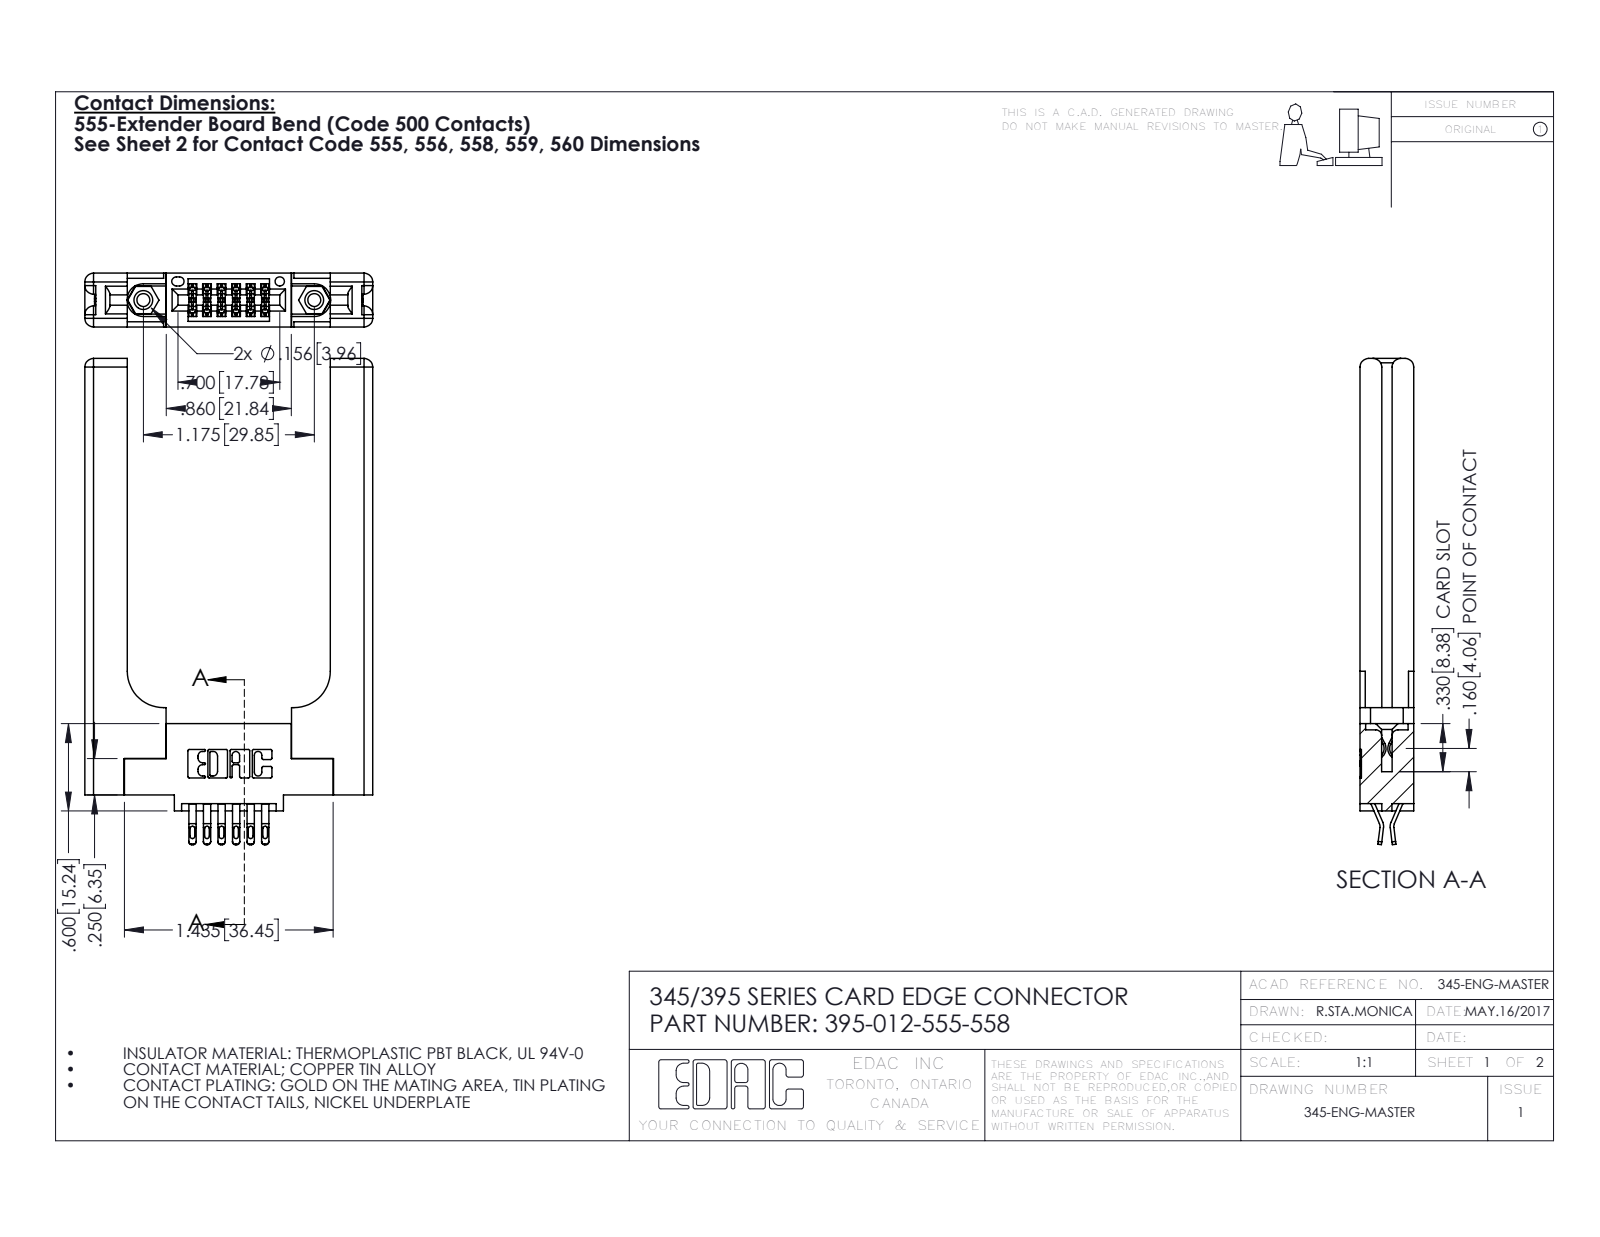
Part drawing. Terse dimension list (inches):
name: 395-012-555-558; 345 Part_0.110 Offset - 0.156 Dia-TH; 345-292-001_555 Tail; 345-250-001_345-250-001-102 (+1 more)
written by: SolidWorks 2016 (CONFIG_CONTROL_DESIGN)
unit: in
bodies: 17 solids, 1058 faces (604 planar, 394 cylindrical, 60 other)
size: 3.342 × 1.979 × 0.37
volume: 0.792 in³; area: 17.43 in²
holes: 2× ⌀0.089, 2× ⌀0.125, 2× ⌀0.156, 1× ⌀0.064
bosses: 2× ⌀0.155
rounds: 30× R0.016, 24× R0.02, 22× R0.01, 18× R0.006, 16× R0.06, 6× R0.007, 6× R0.031, 3× R0.026
face distances: 0.37, 0.15, 0.22, 0.072, 0.148, 0.077, 1.396, 0.298, 0.071, 0.292
hole spacings: 0.27, 0.946, 1.175
